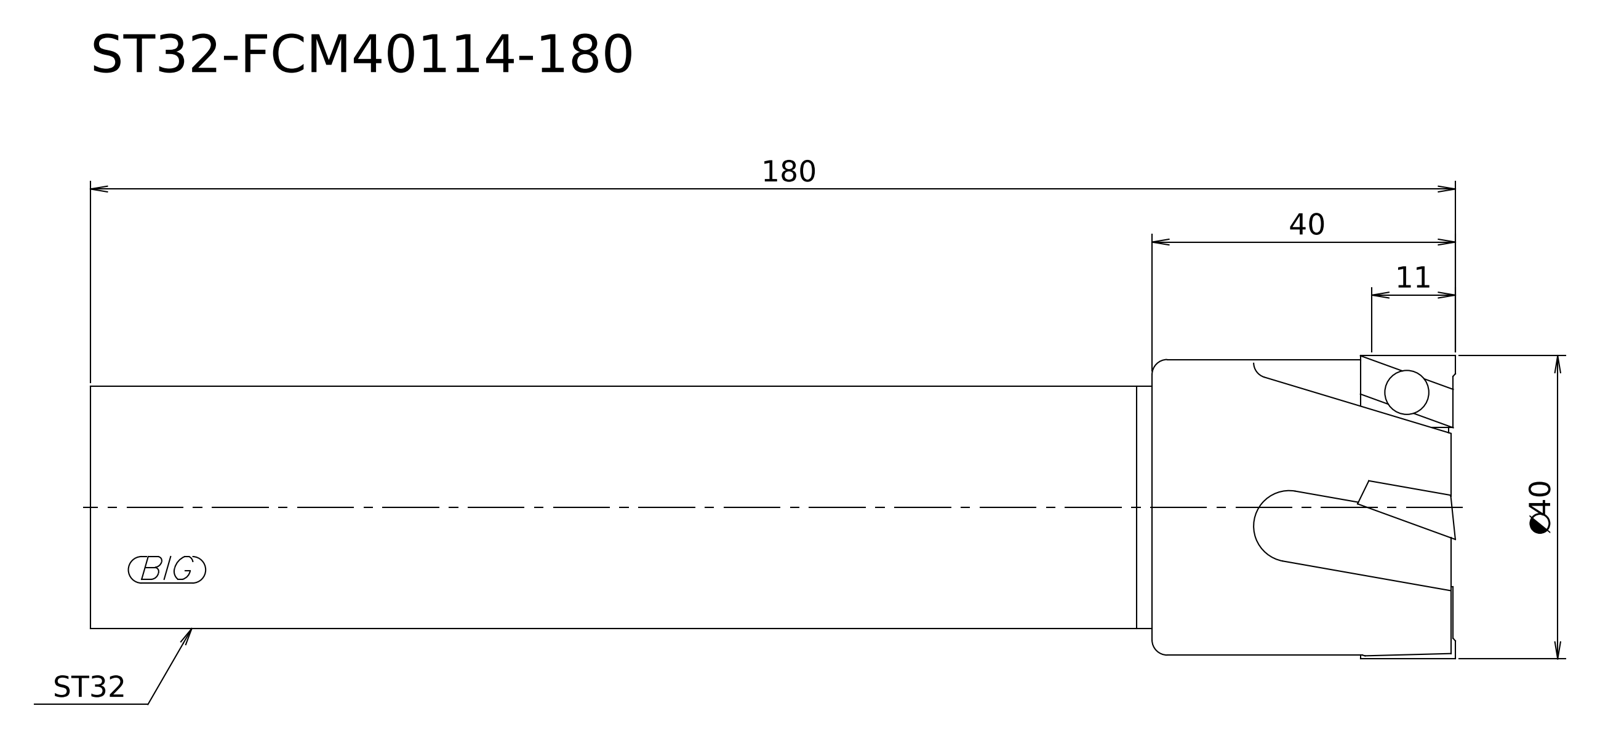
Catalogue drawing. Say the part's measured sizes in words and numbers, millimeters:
Its 3-D file was written by "Kubotek KeyCreator V8.5.1 (14335) (CONFIG_CONTROL_DESIGN)". It is 1 solid with 7 faces: 4 planar, 3 cylindrical and 0 other. Overall it measures 180 by 40 by 40 millimeters. Its volume is 160 843 cubic millimeters and its surface area 21 512 square millimeters. Round bosses or shafts: 1 of diameter 40, 1 of diameter 38.8, 1 of diameter 32. The main face-to-face distances are 180, 40, 140, 12.85, 27.15, 167.15.
